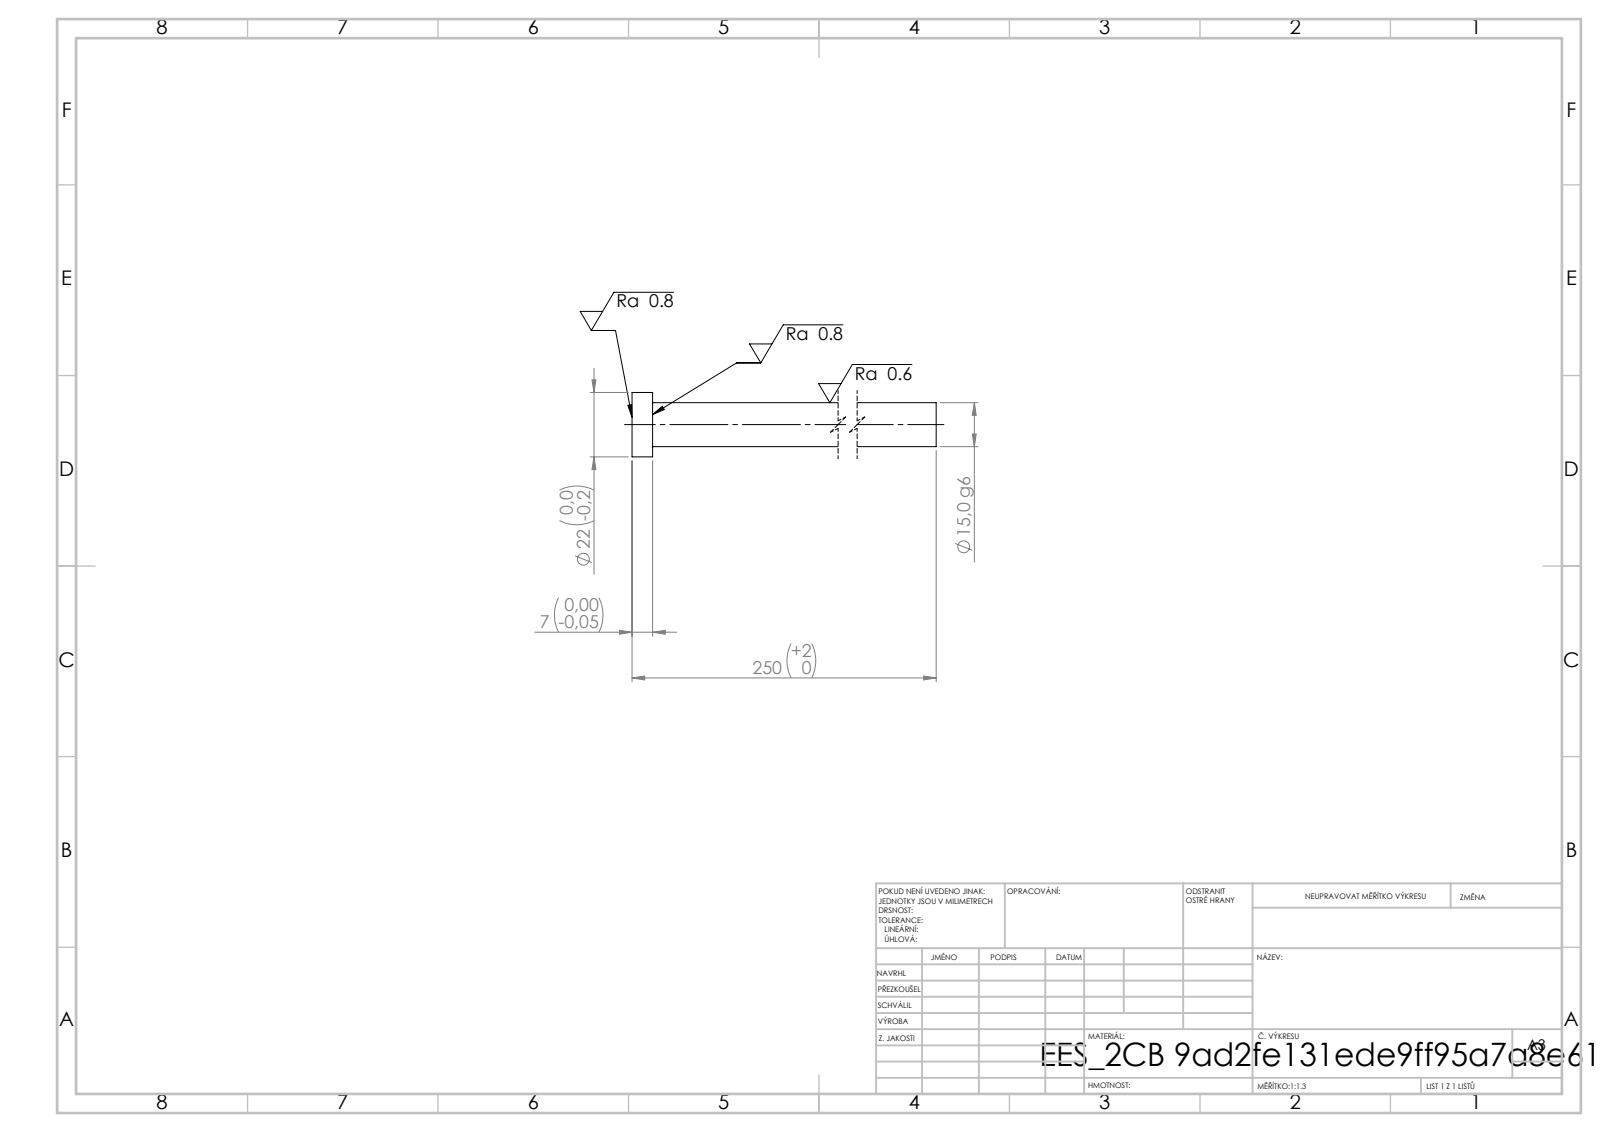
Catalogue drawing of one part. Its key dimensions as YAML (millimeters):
step_written_by: "SolidWorks 2019 (CONFIG_CONTROL_DESIGN)"
units: millimeters
bodies: {solids: 1, faces: 7, planar: 3, cylindrical: 4, other: 0}
overall_size: [250, 22, 22]
volume: 45603
surface_area: 12695
round_bosses_or_shafts:
  - {diameter: 22, count: 1}
  - {diameter: 15, count: 1}
face_to_face_distances: [7, 250, 243]
